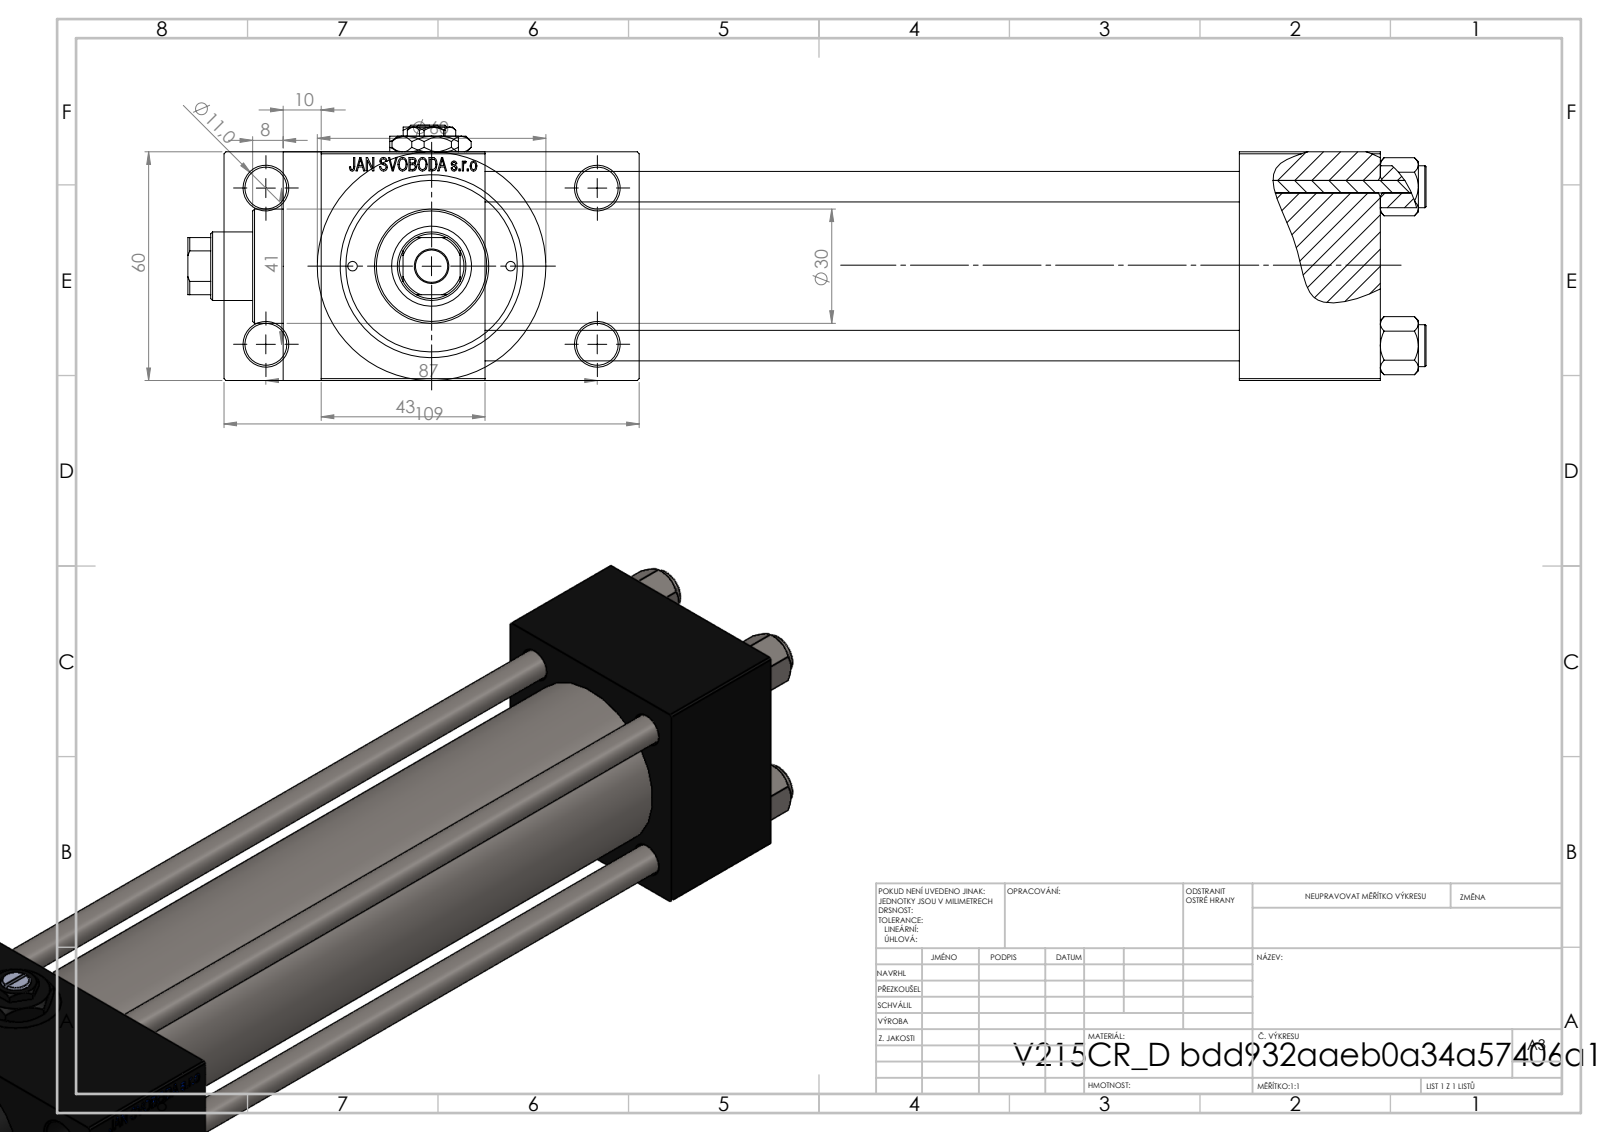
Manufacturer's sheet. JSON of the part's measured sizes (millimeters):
{"part_name": "V215_VC_A; V215CR_VCP_D; V215CR_D_Body; NUT_M5_D (+2 more)", "step_written_by": "SolidWorks 2019 (CONFIG_CONTROL_DESIGN)", "units": "millimeters", "bodies": {"solids": 12, "faces": 1160, "planar": 524, "cylindrical": 96, "other": 540}, "overall_size": [325, 109, 67], "volume_mm3": 632388, "surface_area_mm2": 183231, "round_holes": [[8, 4], [11, 4], [16.66, 3], [24, 3], [2.5, 2], [7, 2], [8.5, 1], [18, 1], [21, 1], [31, 1], [40, 1], [45, 1]], "round_bosses_or_shafts": [[11, 4], [60, 1], [46, 1], [30, 1]], "partial_cylinders_radius": [[8.5, 1]], "face_to_face_distances": [60, 198, 24.5, 84.5, 37, 235, 43, 278, 241, 10], "hole_center_spacings": [20.85, 22.65, 29.49, 30.62, 41.7, 46.53, 47.15, 48.09]}
